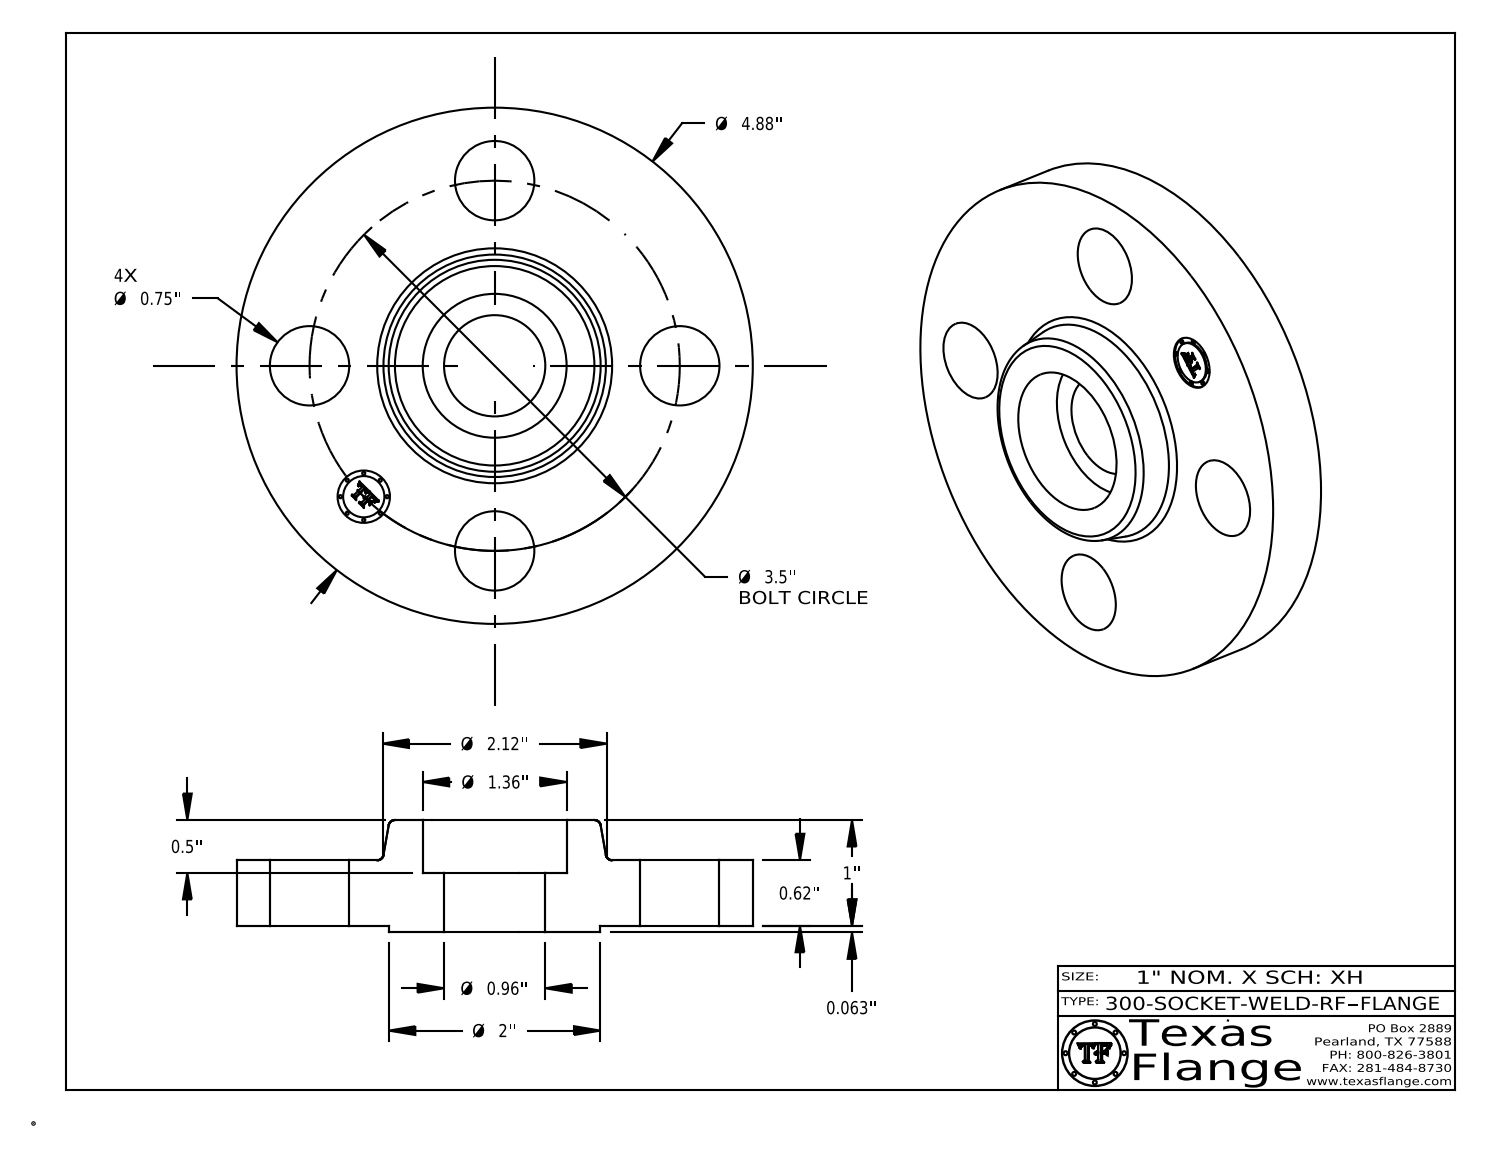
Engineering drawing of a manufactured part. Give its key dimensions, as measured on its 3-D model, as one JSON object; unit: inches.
{"part_name": "300-SOCKET-WELD-RF", "step_written_by": "CATIA V5 STEP AP214 (AUTOMOTIVE_DESIGN)", "units": "inches", "bodies": {"solids": 1, "faces": 412, "planar": 370, "cylindrical": 36, "other": 6}, "overall_size": [4.88, 4.88, 1.063], "volume_in3": 10.82, "surface_area_in2": 53.93, "round_holes": [[0.75, 4], [0.495, 1], [0.957, 1], [1.36, 1]], "round_bosses_or_shafts": [[0.03, 8], [4.88, 1], [2, 1], [0.39, 1]], "face_to_face_distances": [0.62, 0.063, 0.683, 0.5, 1.063, 1, 0.38, 0.563, 0.12, 0.105], "hole_center_spacings": [1.75, 2.475, 1.339, 3.233, 3.5]}
